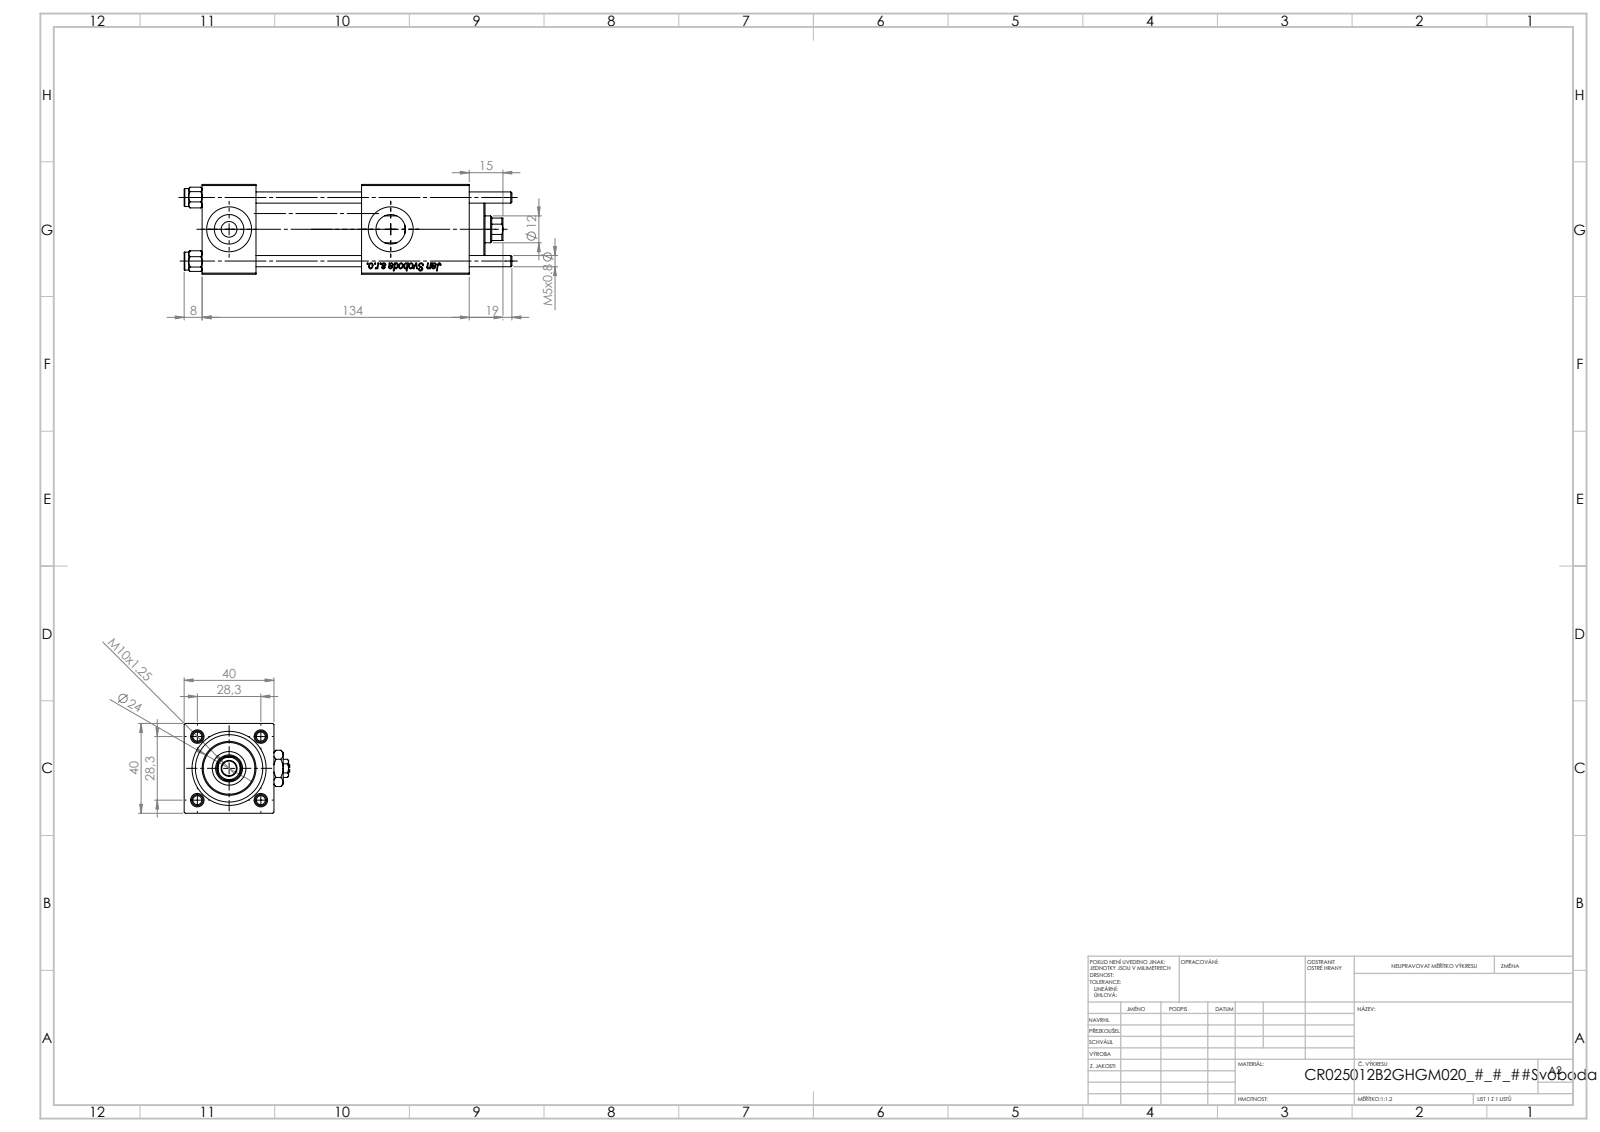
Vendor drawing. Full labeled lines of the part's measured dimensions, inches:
Part name (STEP PRODUCT): V215CR_VCP_B; NUT_M5_B; V215_VC_A; V215CR_B_TYCINKA (+2 more)
STEP written by: SolidWorks 2019 (CONFIG_CONTROL_DESIGN)
Units: inches
Bodies: 12 solids, 1208 faces (452 planar, 86 cylindrical, 670 other)
Overall size (bounding box): 5.748 × 1.85 × 1.575
Volume: 8.795 in³ · Surface area: 92.45 in²
Round holes (diameter × count): ⌀0.197 ×4, ⌀0.787 ×3, ⌀0.276 ×2, ⌀0.518 ×2, ⌀0.256 ×1, ⌀0.472 ×1, ⌀0.591 ×1, ⌀0.984 ×1, ⌀1.181 ×1
Round bosses / shafts (diameter × count): ⌀0.315 ×4, ⌀1.22 ×1, ⌀0.945 ×1
Partial cylindrical surfaces — rounded edges, fillets, slot ends (radius × count): R0.217 ×1
Main face-to-face distances: 1.575, 0.945, 3.555, 2.61, 4.685, 1.85, 2.795, 0.76, 3.74, 1.89
Hole centre spacings: 0.788, 1.114, 1.576, 2.835
